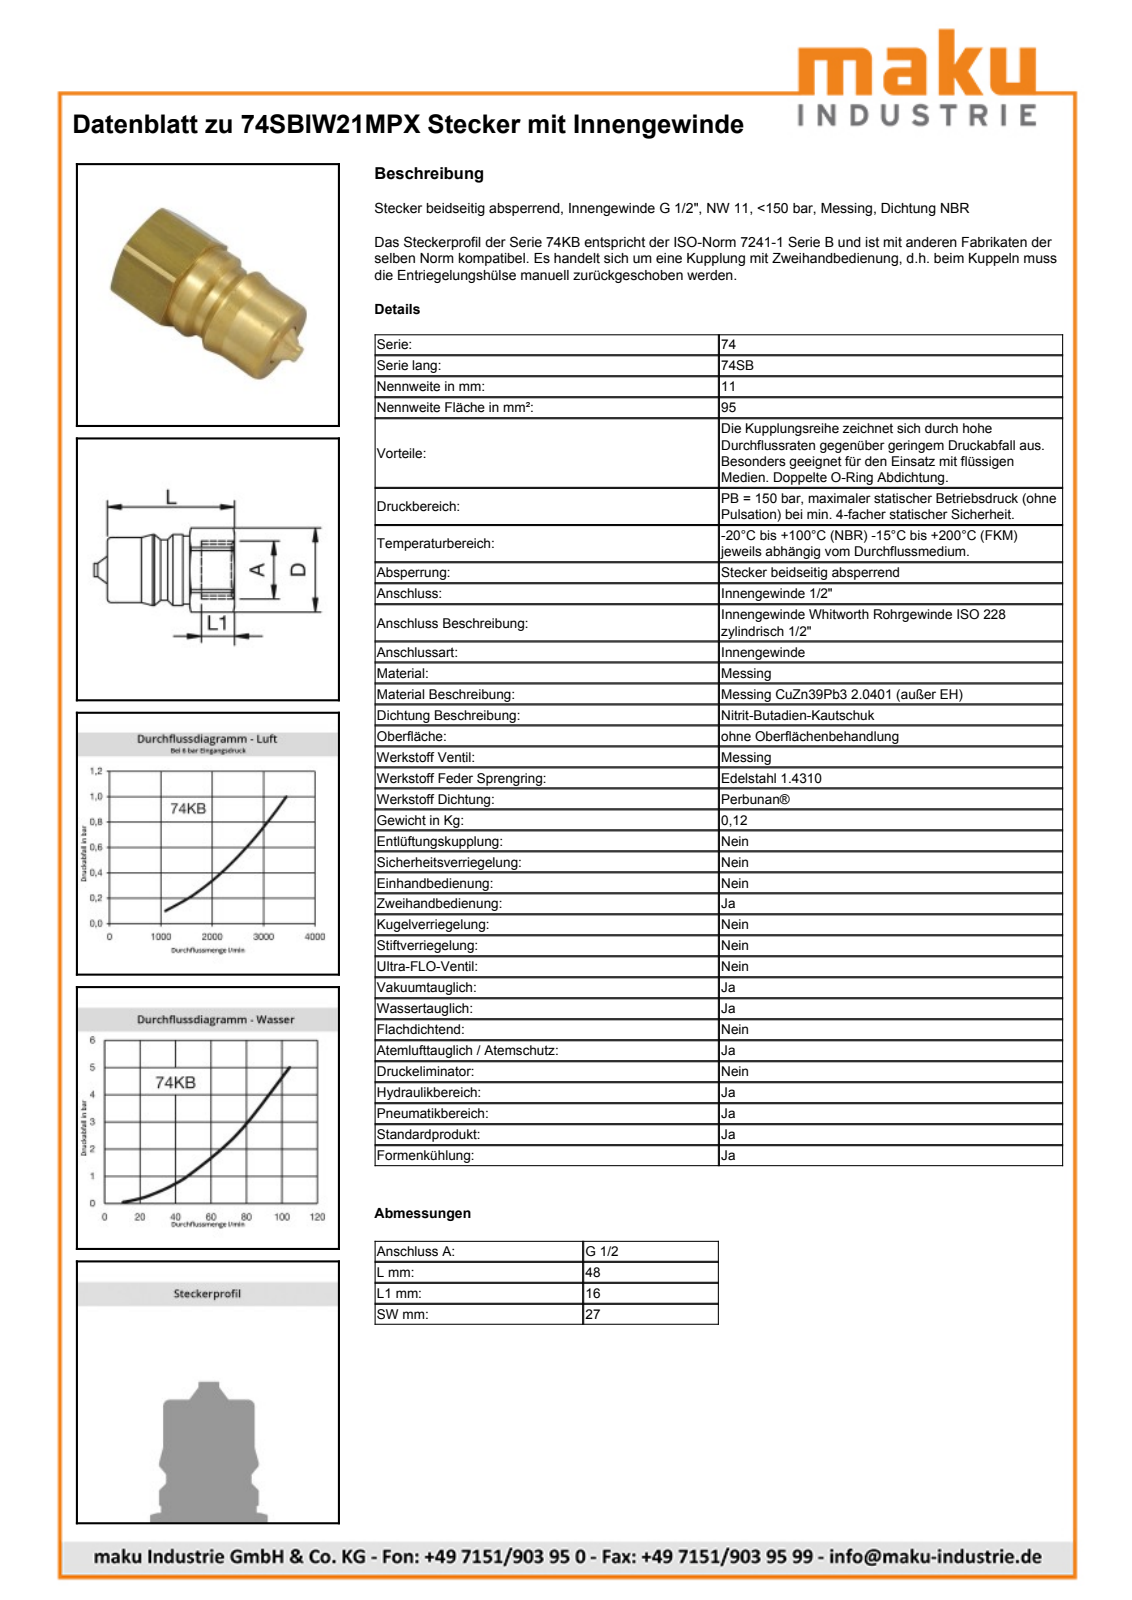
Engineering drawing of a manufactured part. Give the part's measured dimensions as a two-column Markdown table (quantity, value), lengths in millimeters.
| quantity | value |
| --- | --- |
| part name | D107754 |
| STEP written by | Autodesk Inventor 2013 (AUTOMOTIVE_DESIGN) |
| units | millimeters |
| bodies | 1 solid, 47 faces (13 planar, 14 cylindrical, 20 other) |
| overall size | 53.42 × 30.45 × 27 |
| volume | 20 711 mm³ |
| surface area | 6 189 mm² |
| round holes (diameter × count) | 17.3 × 1, 18.63 × 1 |
| round bosses / shafts (diameter × count) | 25.7 × 1, 24.6 × 1, 23.5 × 1, 21.9 × 1, 4.8 × 1 |
| partial cylindrical surfaces (radius × count) | 15.22 × 1 |
| main face-to-face distances | 27, 31.99, 48, 16.01, 29.8, 2.19, 18.2, 32, 2.2, 16 |
